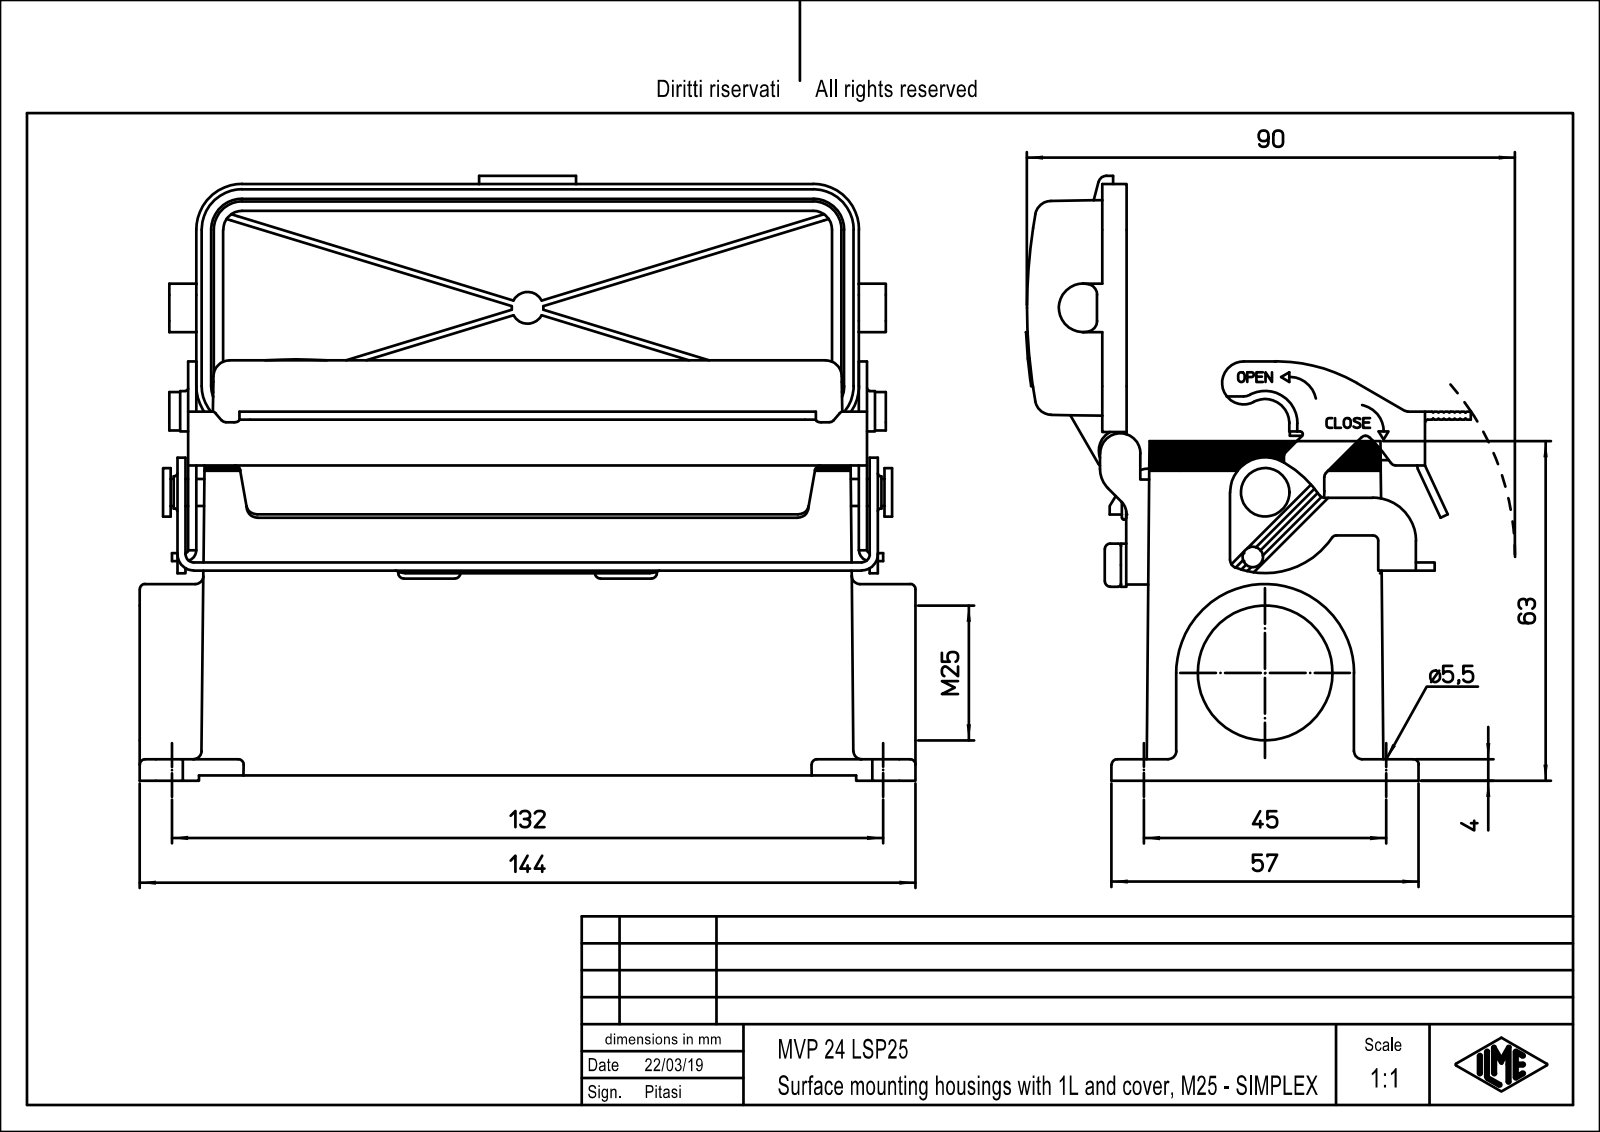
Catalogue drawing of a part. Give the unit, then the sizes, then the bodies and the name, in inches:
Units: inches
Overall size (bounding box): 5.669 × 4.438 × 3.138
Round holes (diameter × count): ⌀0.097 ×4, ⌀0.118 ×4, ⌀0.217 ×4, ⌀0.818 ×1, ⌀0.984 ×1
Round bosses / shafts (diameter × count): ⌀0.031 ×3, ⌀0.354 ×1, ⌀0.331 ×1, ⌀0.315 ×1, ⌀0.236 ×1, ⌀0.197 ×1, ⌀0.094 ×1
Partial cylindrical surfaces — rounded edges, fillets, slot ends (radius × count): R0.079 ×20, R0.118 ×15, R0.059 ×8, R0.138 ×7, R0.039 ×5, R0.236 ×5, R0.02 ×4, R0.071 ×4
Main face-to-face distances: 0.157, 1.594, 1.752, 1.437, 0.059, 0.463, 0.079, 1.587, 4.744, 2.765
Hole centre spacings: 0.655, 1.521, 4.659, 4.857, 1.063, 1.772, 4.094, 4.23
Volume: 9.51 in³ · Surface area: 144.7 in²
Bodies: 1 solid, 616 faces (385 planar, 207 cylindrical, 24 other)
Part name (STEP PRODUCT): MVP_24_LSP25
STEP written by: PTC Creo Elements/Direct Modeling 19.0E 27-Jun-2016 (C) Parametric Technology GmbH (AUTOMOTIVE_DESIGN)
